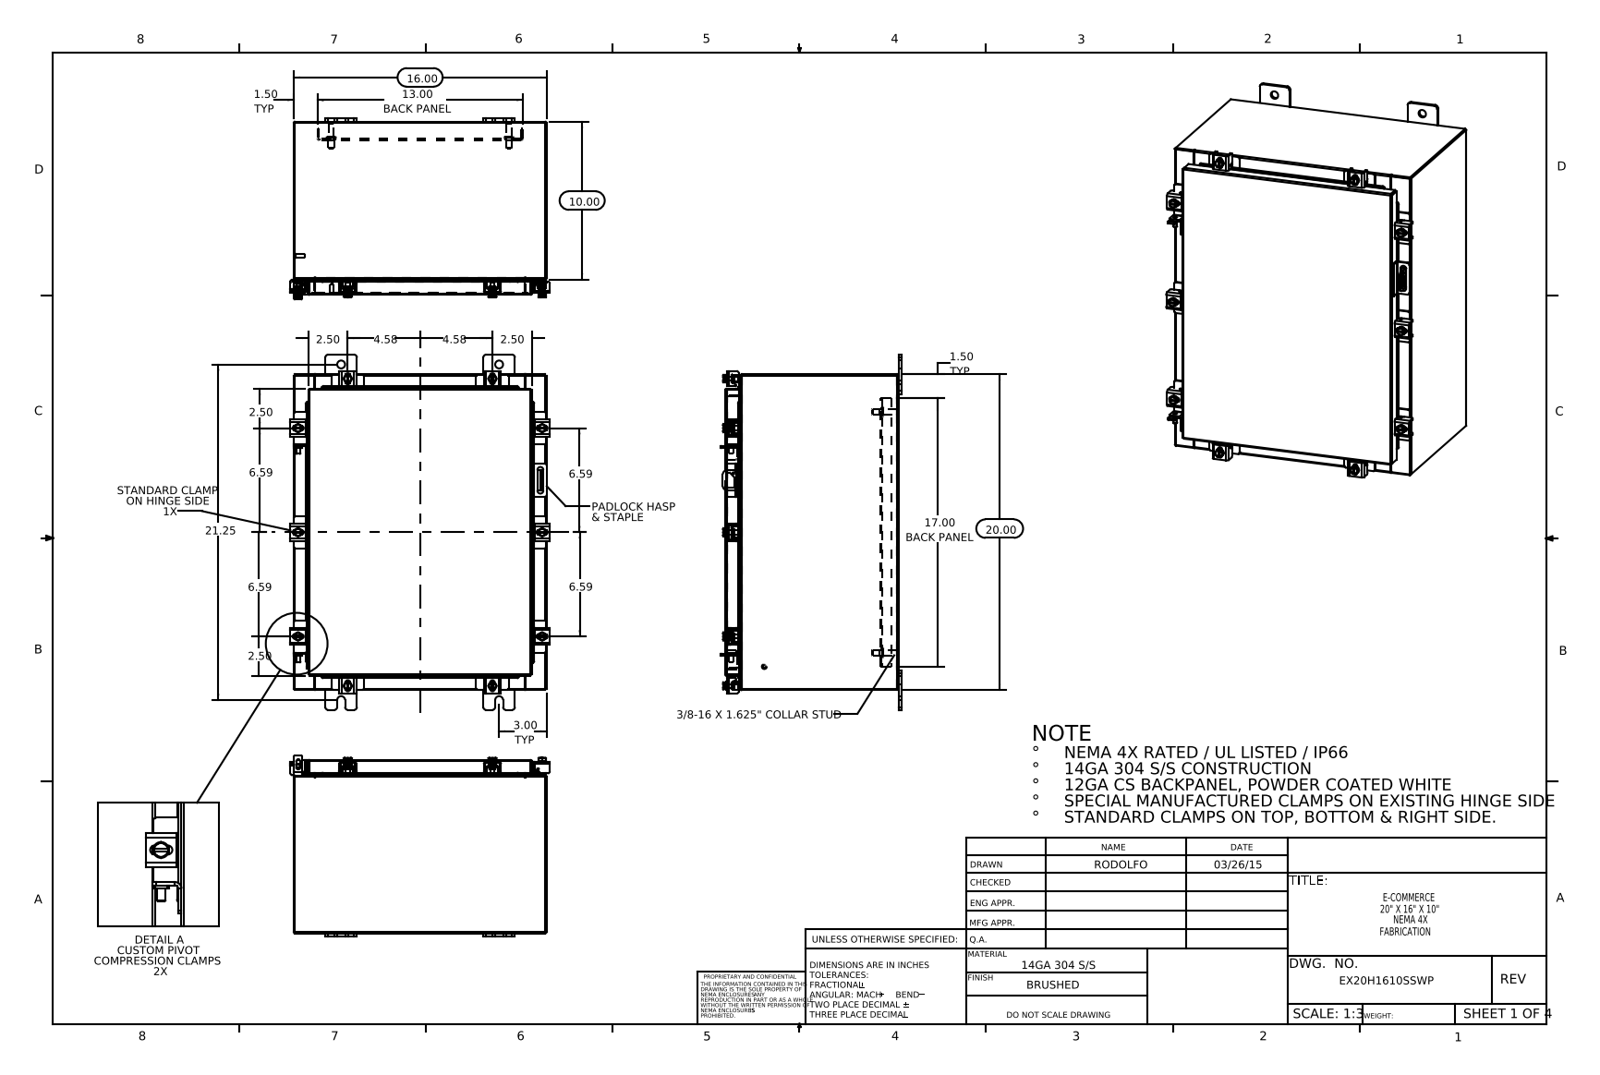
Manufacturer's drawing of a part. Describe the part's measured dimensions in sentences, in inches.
The part is named "EX20H1610SSWP Clamp Bracket; EX20H1610SSWP; ATEX CLAMP HINGE BRAKET; EX20H1610SSWP Mounting Studs (+8 more)". Its 3-D file was written by "SolidWorks 2014 (CONFIG_CONTROL_DESIGN)". It is 71 solids with 1784 faces: 955 planar, 685 cylindrical and 144 other. Overall it measures 22.5 by 16.421 by 11.453 inches. Its volume is 146.1 cubic inches and its surface area 3 692 square inches. Round holes: 10 of diameter 0.213, 10 of diameter 0.26, 8 of diameter 0.5, 1 of diameter 0.125, 1 of diameter 0.25. Round bosses or shafts: 10 of diameter 0.5, 10 of diameter 0.25, 8 of diameter 0.399, 4 of diameter 0.625, 4 of diameter 0.375, 4 of diameter 0.33, 2 of diameter 0.315, 2 of diameter 0.236. Partial cylindrical surfaces (rounded edges, fillets, slot ends): 46 of radius 0.06, 24 of radius 0.013, 24 of radius 0.19, 22 of radius 0.088, 20 of radius 0.141, 18 of radius 0.12, 16 of radius 0.09, 16 of radius 0.1. The main face-to-face distances are 0.075, 10.9, 15.925, 19.925, 10.975, 10.826, 0.104, 1, 1.075, 9.826. The hole center spacings are 2.347, 4.44, 6.594, 10.222, 12.696, 14.374, 15.683, 16.62.
